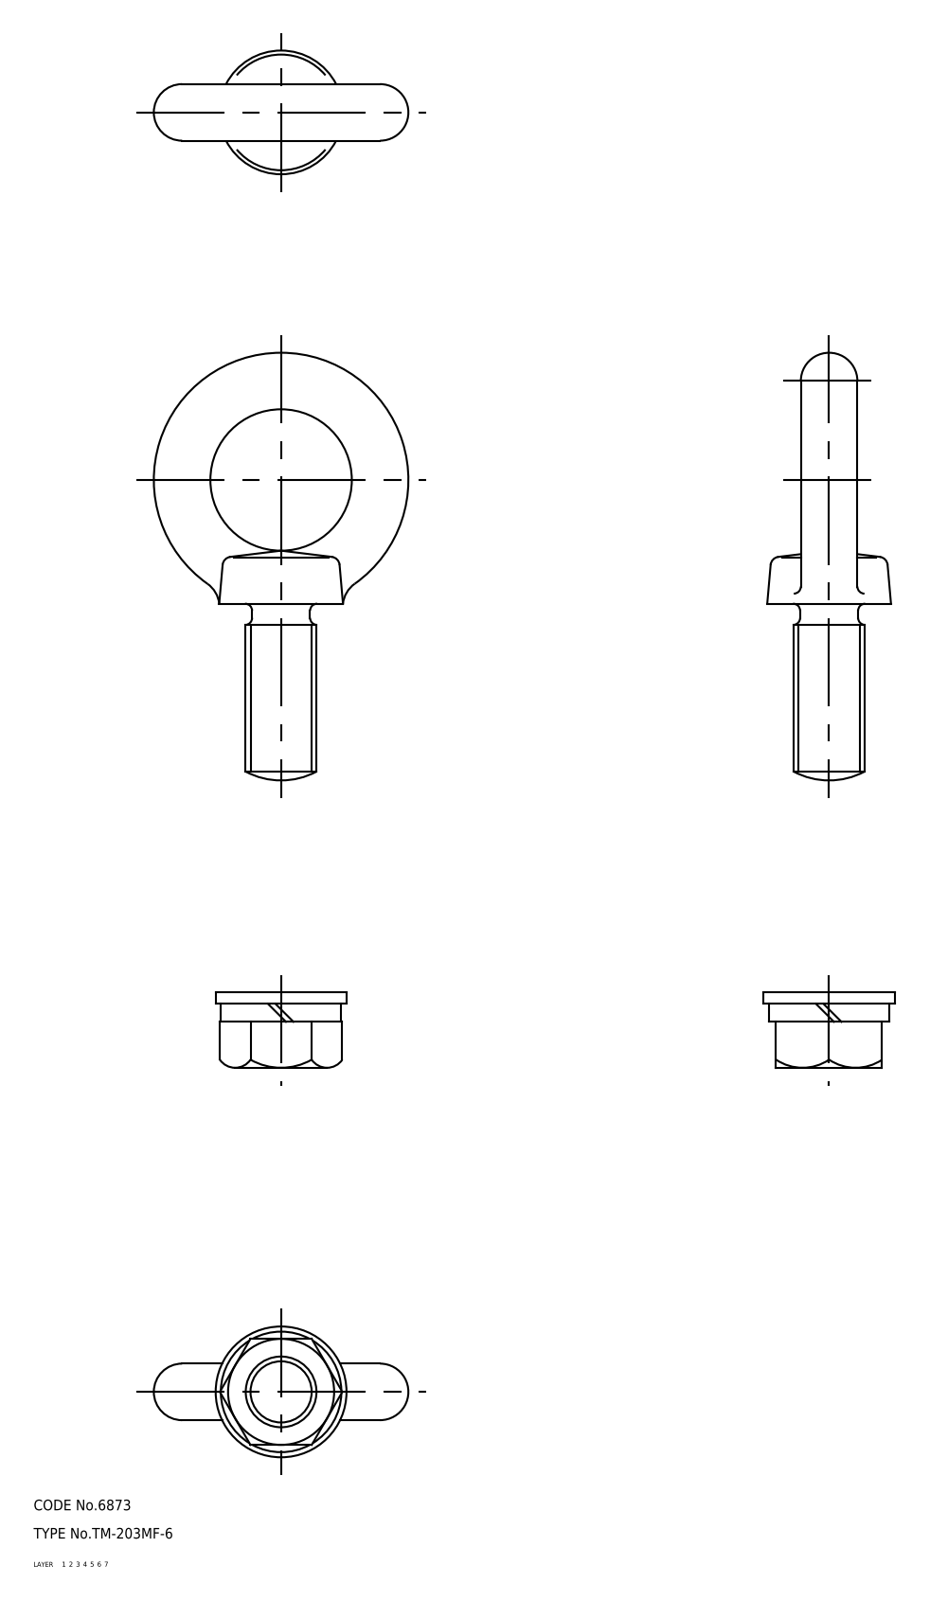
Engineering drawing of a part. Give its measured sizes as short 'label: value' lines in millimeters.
name: TM_203MF_6
written by: SolidWorks 2003240 (AUTOMOTIVE_DESIGN)
unit: mm
bodies: 4 solids, 56 faces (13 planar, 12 cylindrical, 31 other)
size: 121 × 72 × 37
volume: 68 817 mm³; area: 20 348 mm²
holes: 1× ⌀20
bosses: 1× ⌀37, 1× ⌀34.1
face distances: 3.2, 5.1, 8.3, 30, 13, 18.1, 21.3
